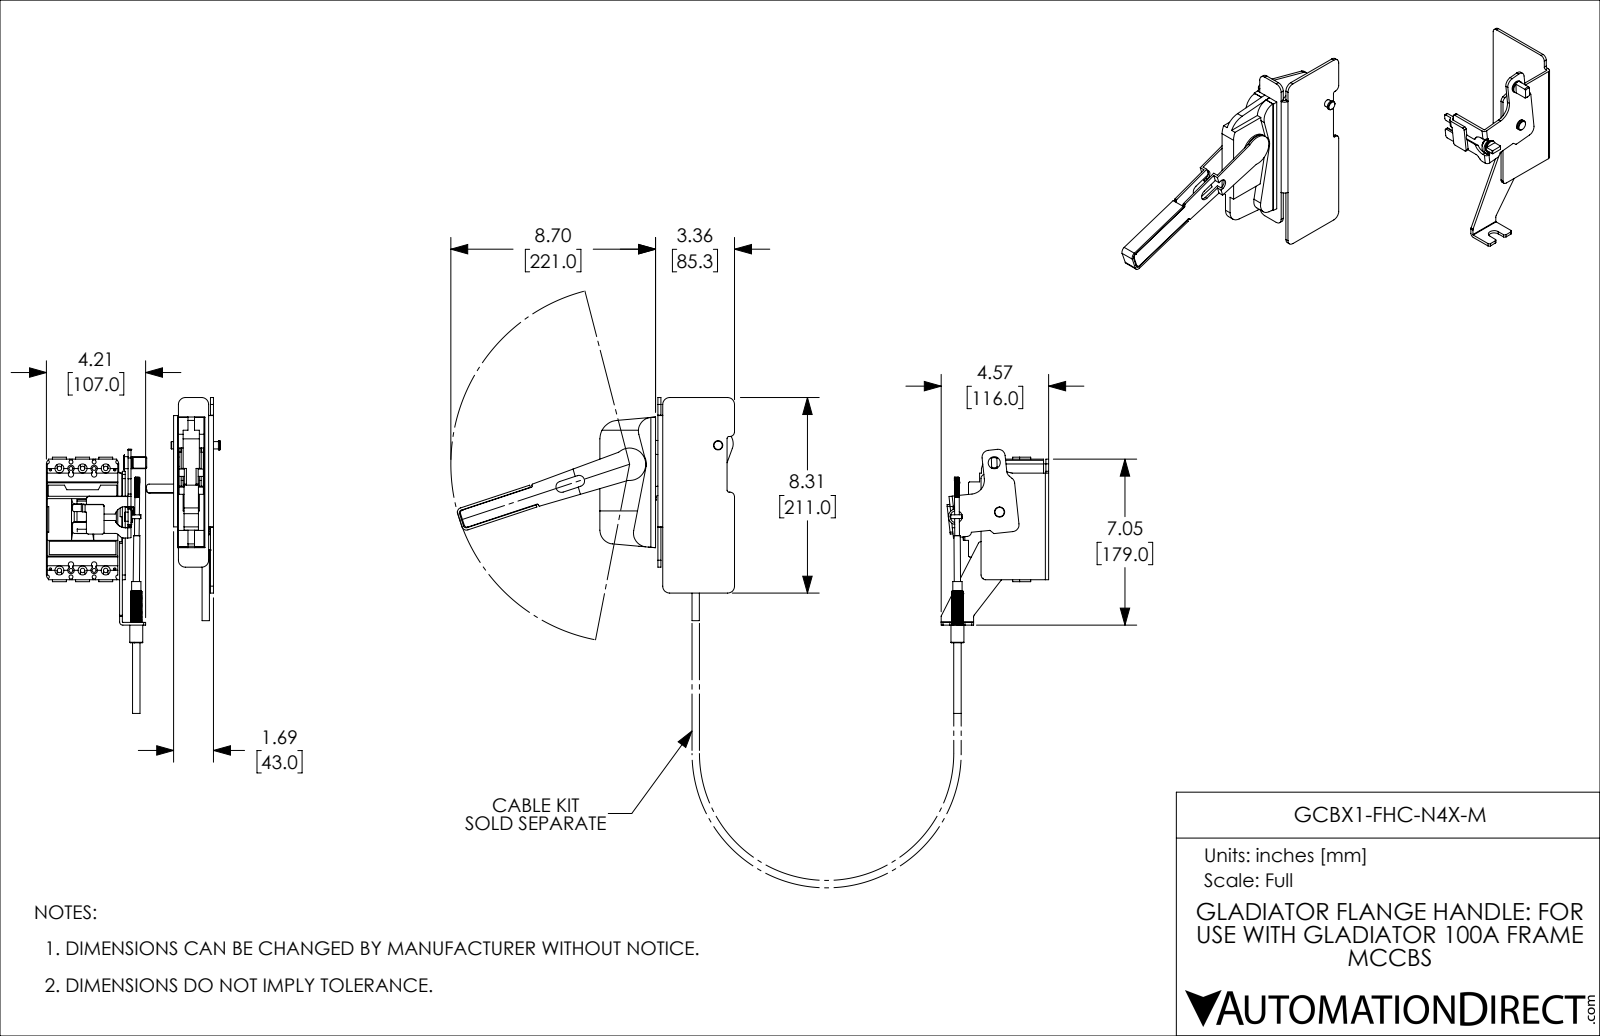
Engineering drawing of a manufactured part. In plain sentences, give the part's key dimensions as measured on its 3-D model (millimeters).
The part is named "GCBX2-CBL-36_2; GCBX1-FHC-N4X-M_1; GCBX1-FHC-N4X-M_2; GCB100S-3FF15LL (+2 more)". Its 3-D file was written by "SolidWorks 2021 (CONFIG_CONTROL_DESIGN)". It is 29 solids with 2036 faces: 1080 planar, 781 cylindrical and 175 other. Overall it measures 638.3 by 340.7 by 187.6 millimeters. Its volume is 1 111 000 cubic millimeters and its surface area 310 800 square millimeters. Round holes: 8 of diameter 4.2, 6 of diameter 4.8, 6 of diameter 9.7, 4 of diameter 2.5, 4 of diameter 7, 2 of diameter 5.1, 2 of diameter 8, 1 of diameter 3, 1 of diameter 6.2, 1 of diameter 6.5, 1 of diameter 11, 1 of diameter 13. Round bosses or shafts: 5 of diameter 10, 2 of diameter 7.3, 2 of diameter 6.7, 2 of diameter 5, 1 of diameter 35, 1 of diameter 14, 1 of diameter 13, 1 of diameter 12. Partial cylindrical surfaces (rounded edges, fillets, slot ends): 86 of radius 0.3, 39 of radius 0.5, 20 of radius 7.5, 18 of radius 1, 18 of radius 3, 17 of radius 5, 16 of radius 2, 14 of radius 4. The main face-to-face distances are 3.2, 3, 5, 9.2, 92.1, 95.1, 98.3, 81, 76, 176.1. The hole center spacings are 12.5, 14.3, 25, 110.7, 117.7, 112.8, 110, 7.
